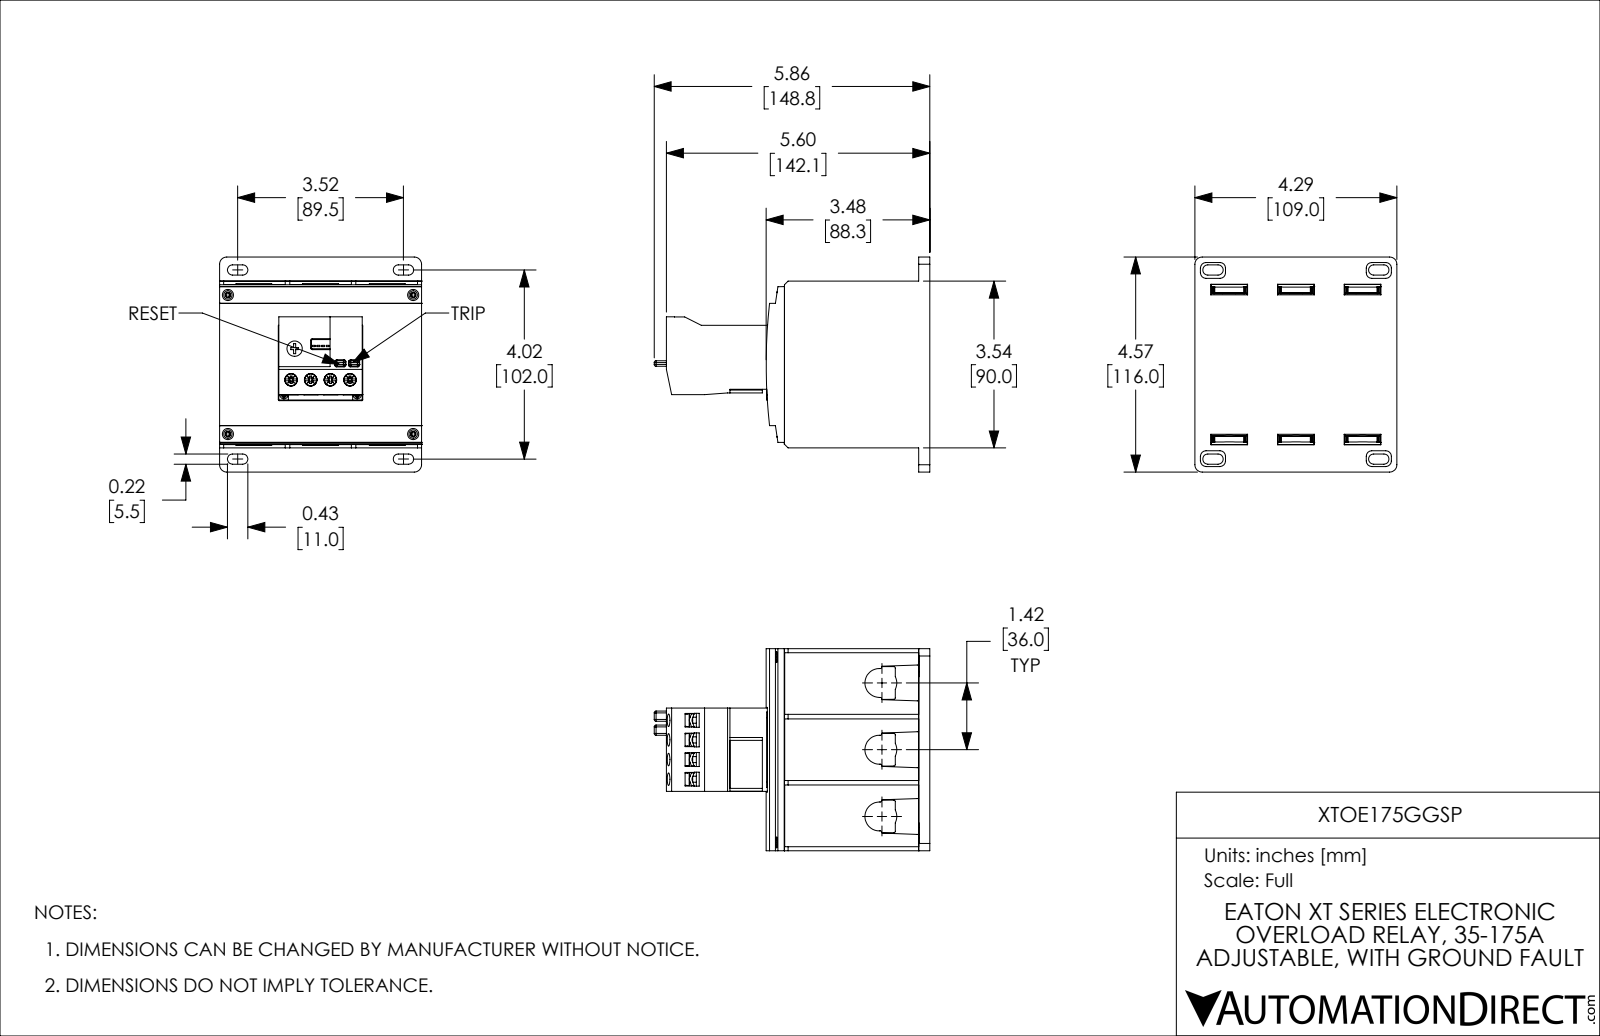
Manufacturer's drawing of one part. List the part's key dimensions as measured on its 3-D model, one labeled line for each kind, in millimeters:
Part name (STEP PRODUCT): XTOE175GGSP
STEP written by: SolidWorks 2018 (AUTOMOTIVE_DESIGN)
Units: millimetres
Bodies: 25 solids, 1031 faces (665 planar, 188 cylindrical, 178 other)
Overall size (bounding box): 148.75 × 116 × 109
Volume: 824 855 mm³ · Surface area: 117 774 mm²
Round holes (diameter × count): ⌀2.8 ×4, ⌀3.55 ×4, ⌀6 ×4, ⌀6.8 ×4, ⌀2.18 ×2, ⌀3.2 ×2
Round bosses / shafts (diameter × count): ⌀4.5 ×6, ⌀3.4 ×4, ⌀3.25 ×4, ⌀2.8 ×4, ⌀2.5 ×4, ⌀8.27 ×1
Partial cylindrical surfaces — rounded edges, fillets, slot ends (radius × count): R0.5 ×33, R1 ×14, R2 ×8, R2.75 ×8, R0.8 ×6, R3.92 ×4, R7.8 ×3, R8 ×3
Main face-to-face distances: 78.48, 109, 32, 77, 72.5, 5.98, 45, 18.6, 12.62, 59.88
Hole centre spacings: 10.6, 21.2, 8.88, 10.59, 10.61, 44.93, 63.96, 80.22
